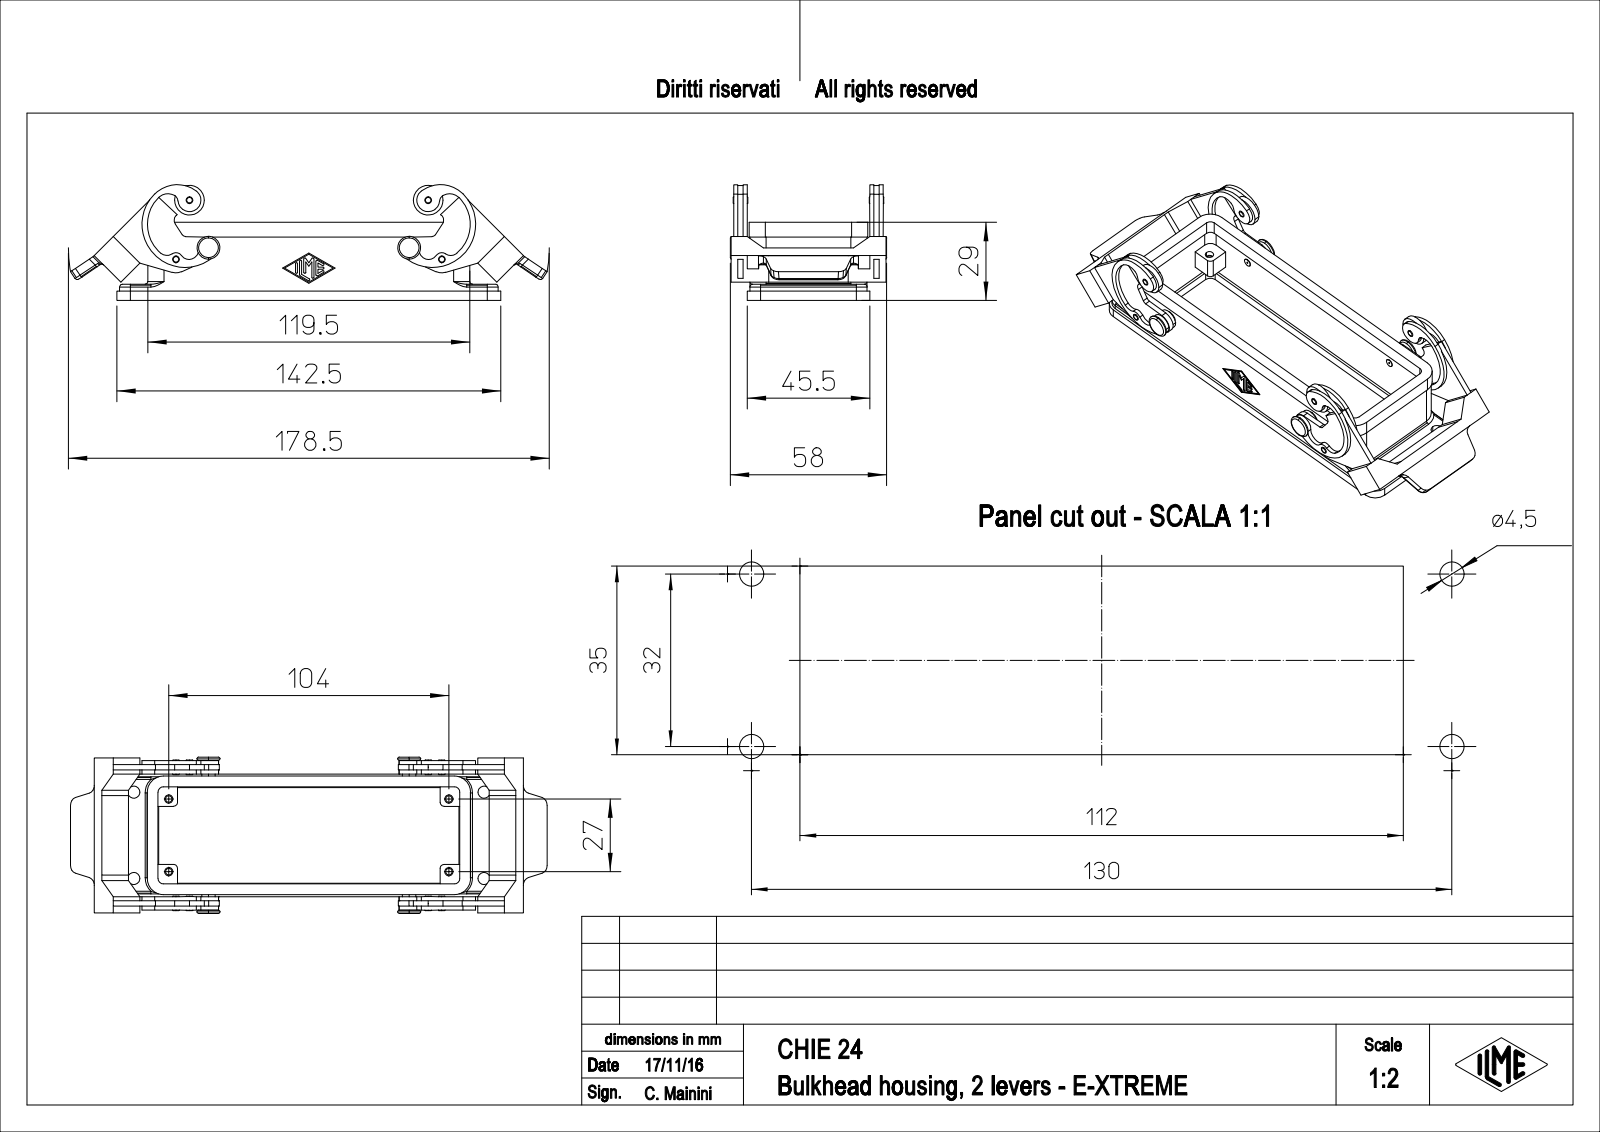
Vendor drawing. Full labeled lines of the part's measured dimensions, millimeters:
Part name (STEP PRODUCT): CHIE_24
STEP written by: PTC Creo Elements/Direct Modeling 19.0E 27-Jun-2016 (C) Parametric Technology GmbH (AUTOMOTIVE_DESIGN)
Units: millimetres
Bodies: 1 solid, 753 faces (327 planar, 334 cylindrical, 92 other)
Overall size (bounding box): 176.99 × 58 × 42.94
Volume: 58 457 mm³ · Surface area: 40 484 mm²
Round holes (diameter × count): ⌀2 ×4, ⌀2.46 ×4, ⌀3.1 ×4, ⌀4.5 ×4, ⌀4.6 ×4, ⌀2.5 ×2
Round bosses / shafts (diameter × count): ⌀11 ×2, ⌀5 ×2, ⌀3 ×2
Partial cylindrical surfaces — rounded edges, fillets, slot ends (radius × count): R0.38 ×14, R1 ×14, R3 ×12, R2.5 ×10, R3.5 ×8, R5 ×8, R6 ×8, R1.5 ×6
Main face-to-face distances: 3, 4, 40.5, 1, 50.5, 3.5, 2.5, 0.75, 1.5, 4.5
Hole centre spacings: 13.24, 32.24, 117.03, 120.66, 22.56, 27, 32, 96.21
